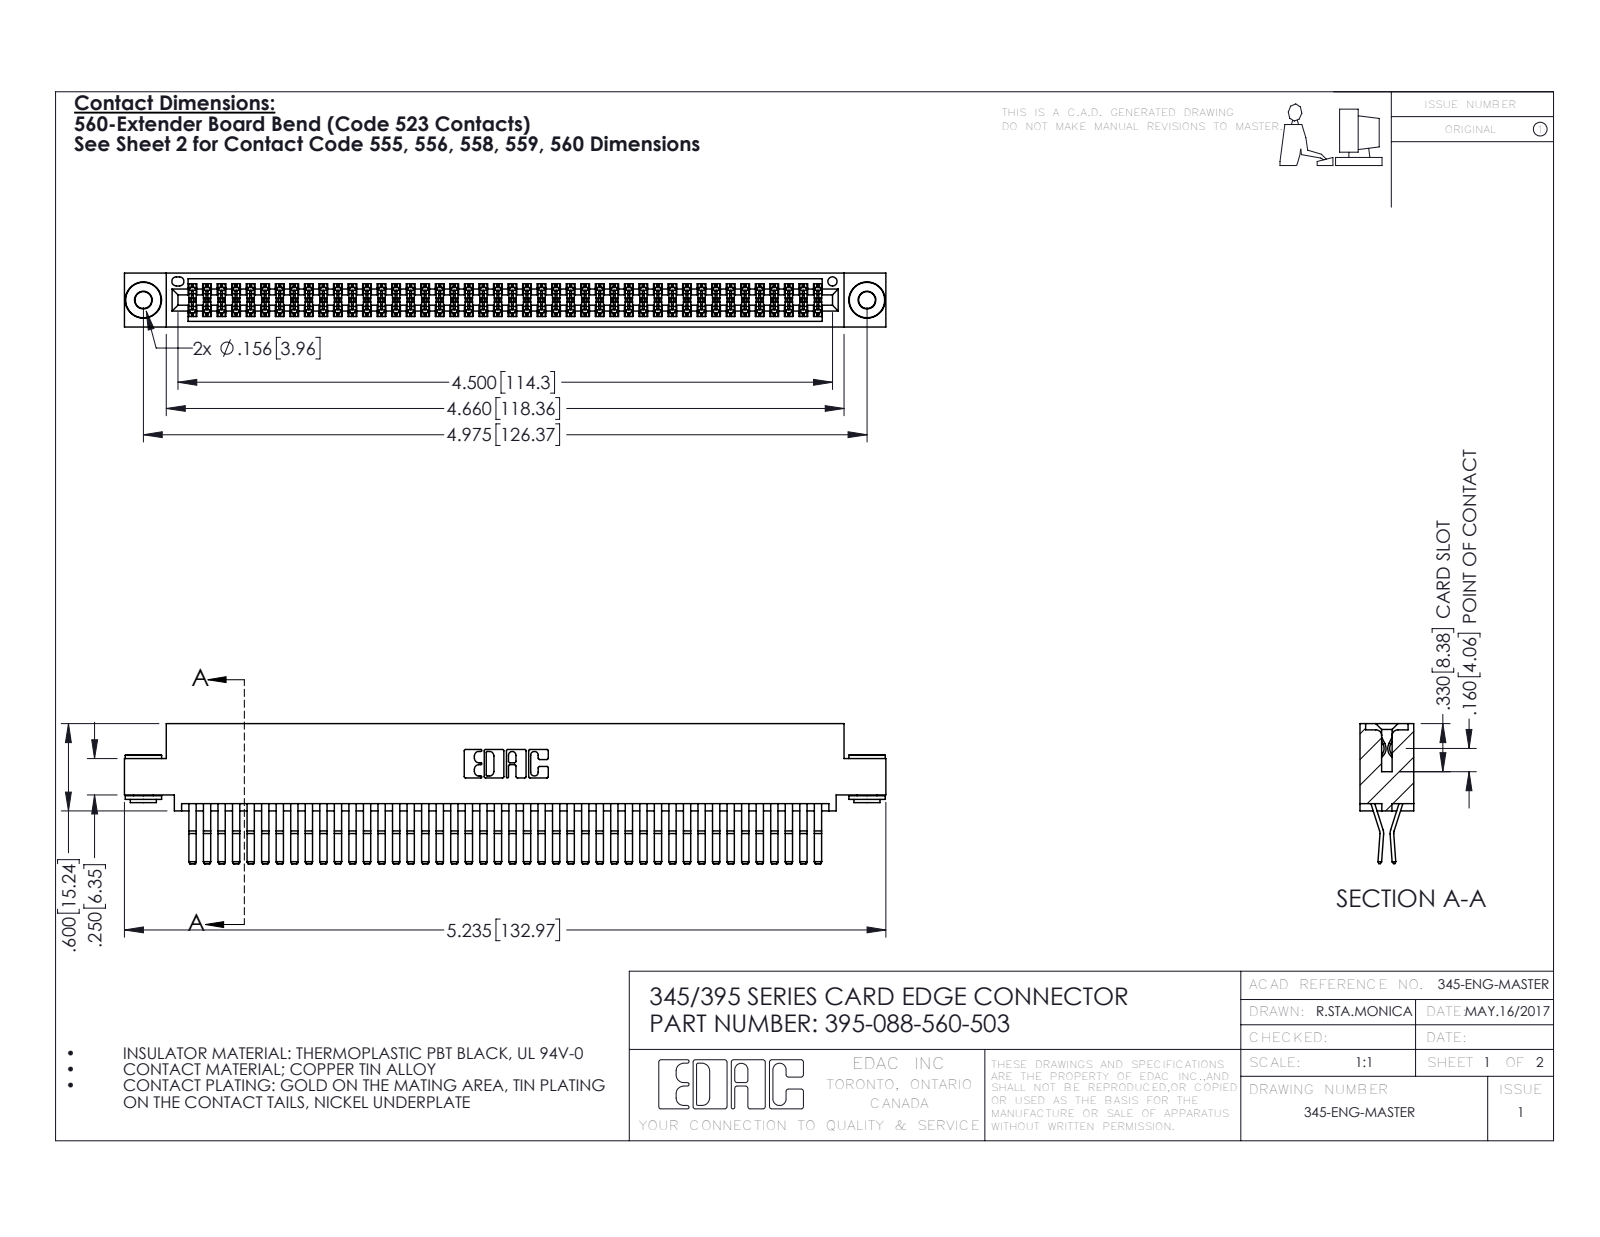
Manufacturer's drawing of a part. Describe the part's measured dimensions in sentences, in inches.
The part is named "345 Part_0.110 Offset - 0.156 Dia-TH; 395-088-560-503; 345-250-002_345-250-002-102; 345-292-001_560 Tail". Its 3-D file was written by "SolidWorks 2016 (CONFIG_CONTROL_DESIGN)". It is 91 solids with 4744 faces: 2998 planar, 1738 cylindrical and 8 other. Overall it measures 5.235 by 0.962 by 0.37 inches. Its volume is 0.821 cubic inches and its surface area 33.66 square inches. Round holes: 2 of diameter 0.116, 2 of diameter 0.156, 1 of diameter 0.064. Round bosses or shafts: 2 of diameter 0.25, 2 of diameter 0.18, 2 of diameter 0.136. Partial cylindrical surfaces (rounded edges, fillets, slot ends): 132 of radius 0.006, 22 of radius 0.01, 6 of radius 0.007, 6 of radius 0.031, 3 of radius 0.026, 2 of radius 0.01, 2 of radius 0.014, 2 of radius 0.019. The main face-to-face distances are 0.025, 0.072, 0.298, 0.37, 0.2, 0.098, 0.272, 0.225, 0.175, 0.149. The hole center spacings are 0.27, 4.739, 4.975.
